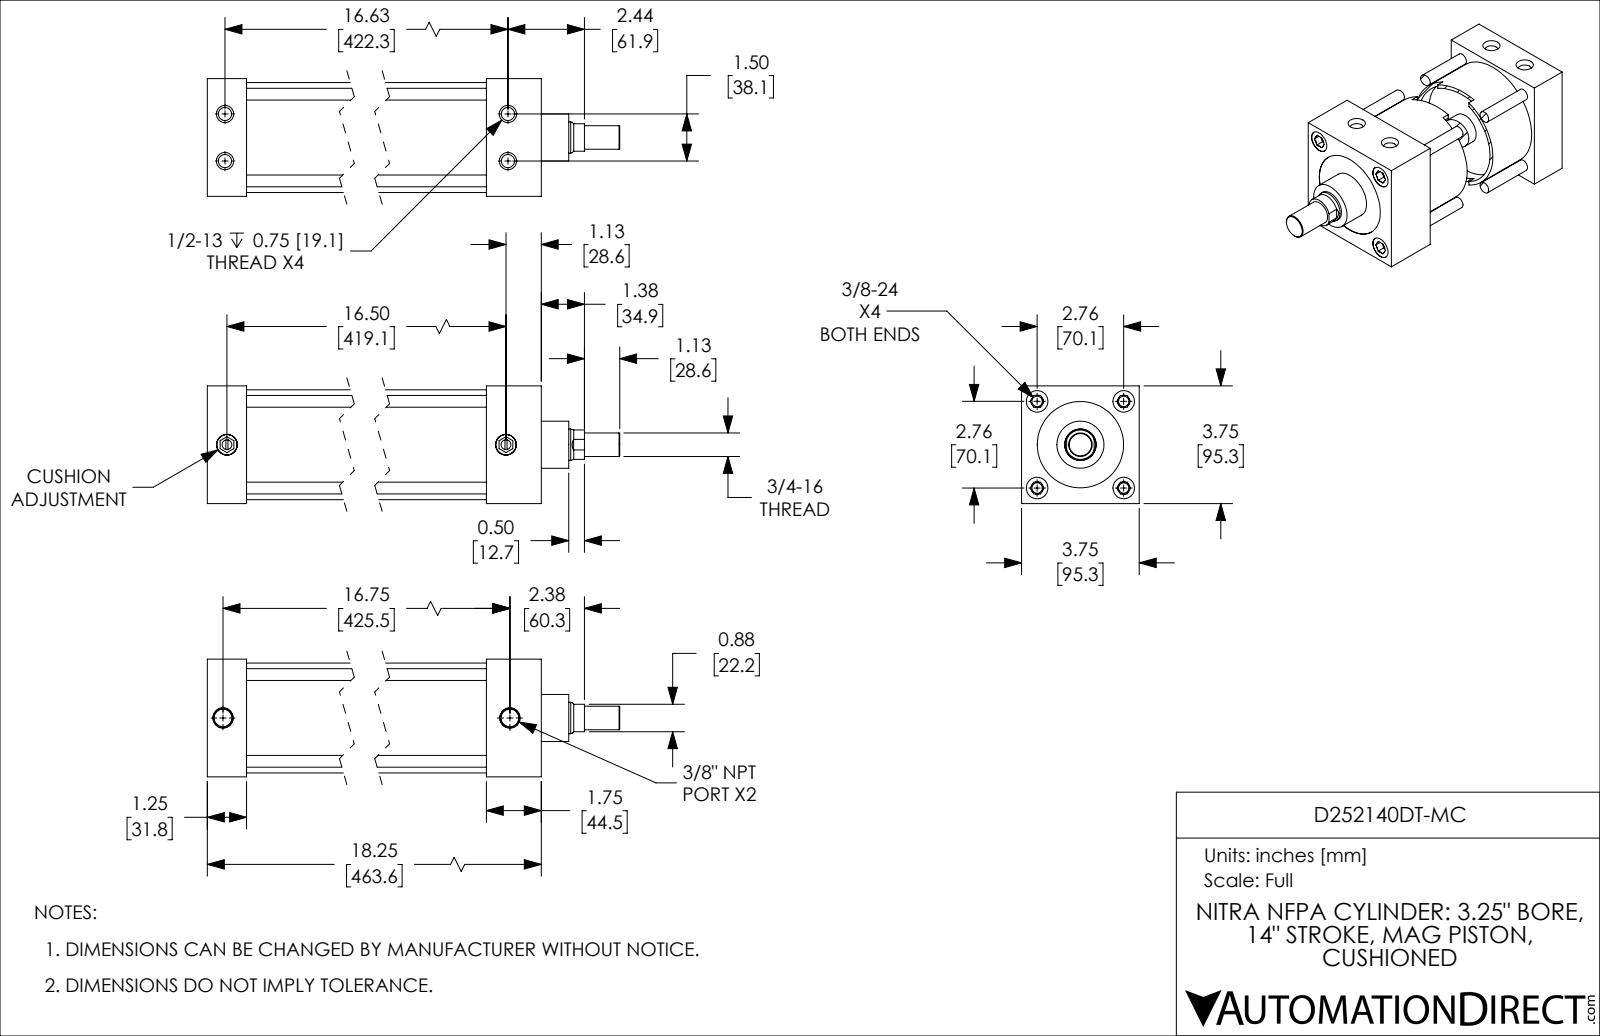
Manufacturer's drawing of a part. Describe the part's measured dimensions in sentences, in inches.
The part is named "D252140DT-MC_PISTON_KK1; D252140DT-MC_BODY; D252140DT-MC; D252140DT-MC_CUSHION". Its 3-D file was written by "SolidWorks 2019 (CONFIG_CONTROL_DESIGN)". It is 4 solids with 246 faces: 90 planar, 78 cylindrical and 78 other. Overall it measures 20.75 by 3.75 by 3.75 inches. Its volume is 90.53 cubic inches and its surface area 612.6 square inches. Round holes: 4 of diameter 0.332, 4 of diameter 0.422, 4 of diameter 0.687, 2 of diameter 0.312, 2 of diameter 0.562, 2 of diameter 0.656, 1 of diameter 1.001, 1 of diameter 2.75, 1 of diameter 3.251. Round bosses or shafts: 4 of diameter 0.375, 2 of diameter 0.657, 1 of diameter 3.501, 1 of diameter 3.249, 1 of diameter 1.5, 1 of diameter 0.999, 1 of diameter 0.75. Partial cylindrical surfaces (rounded edges, fillets, slot ends): 1 of radius 0.469. The main face-to-face distances are 1.25, 3.75, 16.5, 15.25, 2.5, 14, 18.25, 17, 15.75, 1.75. The hole center spacings are 0.753, 1.952, 2.76, 16.704, 1.5, 3.903, 16.625, 16.693.
